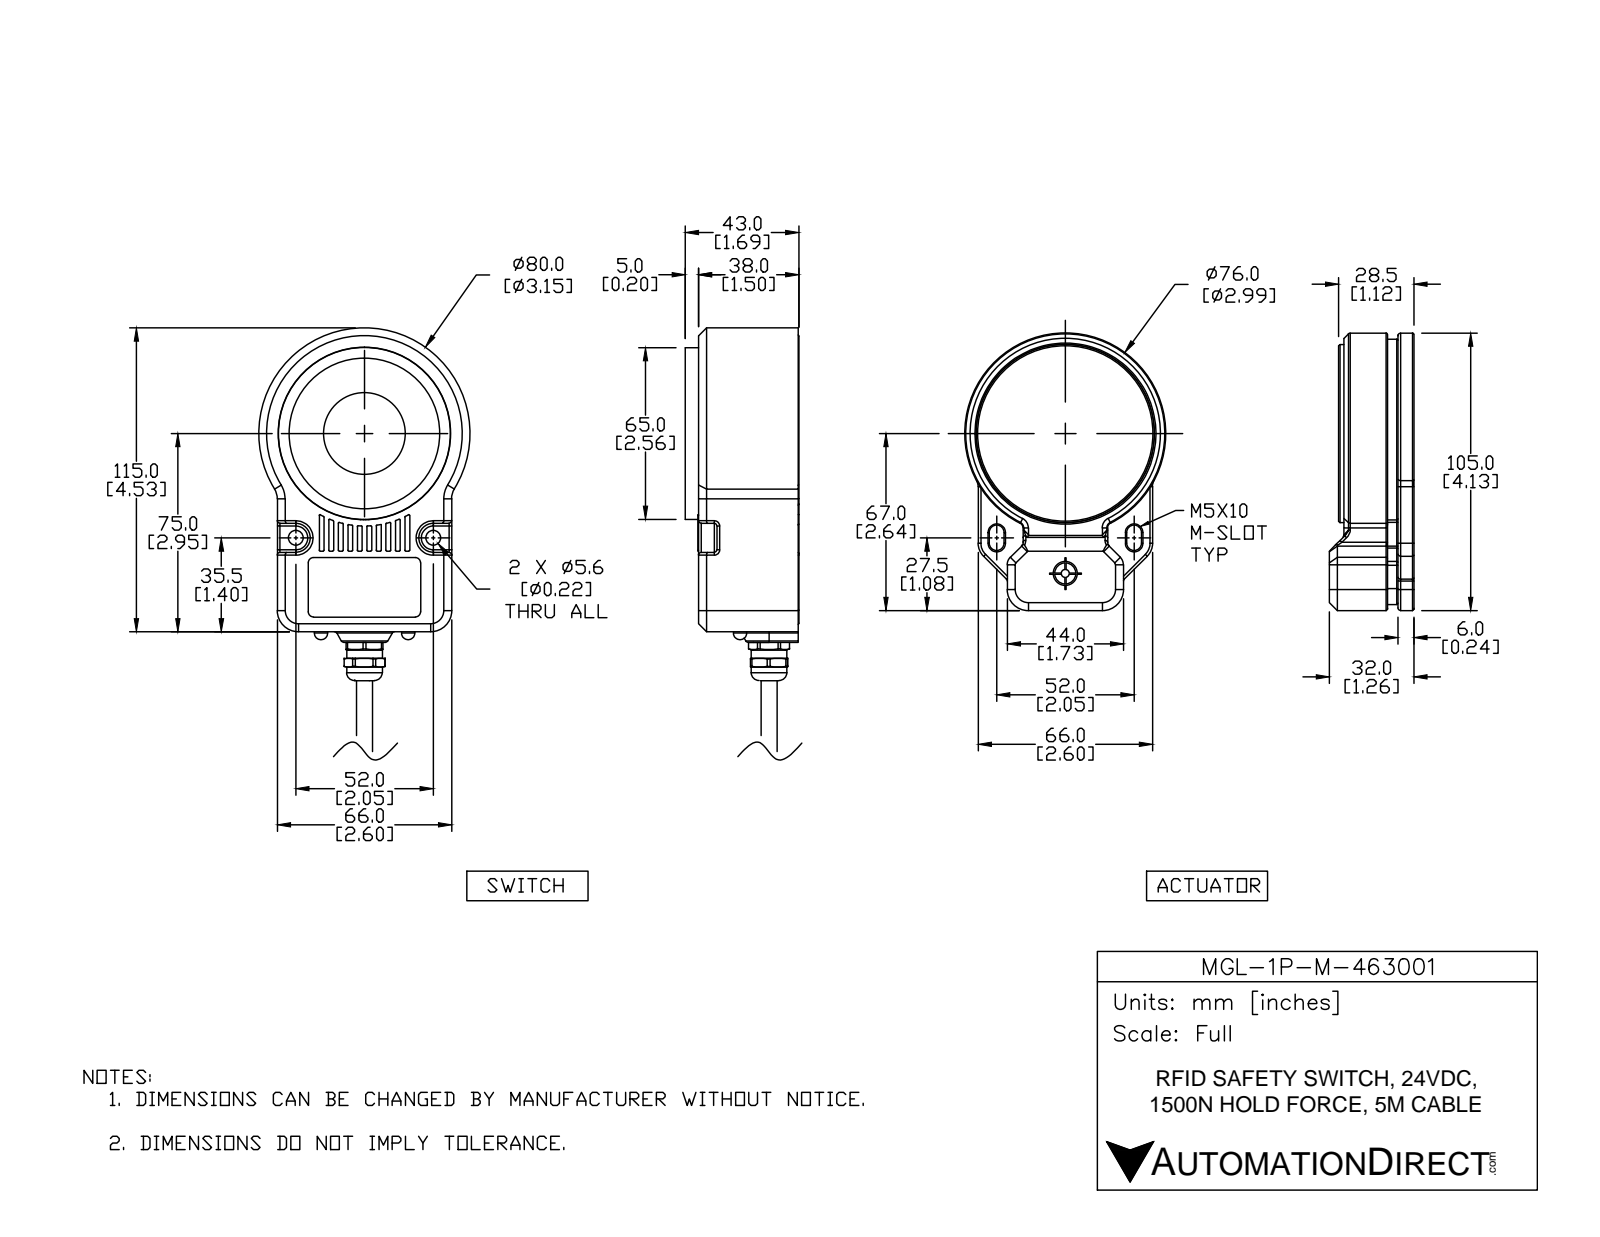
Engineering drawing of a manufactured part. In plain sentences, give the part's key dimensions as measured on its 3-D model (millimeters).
The part is named "MGL-1P-U-463001_1; MGL-1P-U-463001_2; MGL-1P-U-463001". Its 3-D file was written by "SolidWorks 2017 (AUTOMOTIVE_DESIGN)". It is 17 solids with 1674 faces: 449 planar, 708 cylindrical and 517 other. Overall it measures 207.3 by 80 by 72.5 millimeters. Its volume is 310 700 cubic millimeters and its surface area 135 600 square millimeters. Round holes: 6 of diameter 5, 5 of diameter 11.5, 4 of diameter 2.4, 3 of diameter 8, 2 of diameter 2, 2 of diameter 3.3, 2 of diameter 5.6, 2 of diameter 7, 2 of diameter 9, 1 of diameter 4, 1 of diameter 6.4, 1 of diameter 6.8. Round bosses or shafts: 4 of diameter 0.5, 3 of diameter 12, 3 of diameter 2, 2 of diameter 5.8, 2 of diameter 5.4, 2 of diameter 3.9, 2 of diameter 1.2, 1 of diameter 76. Partial cylindrical surfaces (rounded edges, fillets, slot ends): 187 of radius 0.5, 75 of radius 1, 39 of radius 0.3, 18 of radius 2, 7 of radius 0.6, 7 of radius 8, 6 of radius 4, 6 of radius 5.5. The main face-to-face distances are 6, 8, 2.5, 58.5, 66.5, 10.5, 56, 3, 16.5, 72.5. The hole center spacings are 20, 25, 35.4, 34.6, 4.4, 8.9, 10.2, 10.3.
